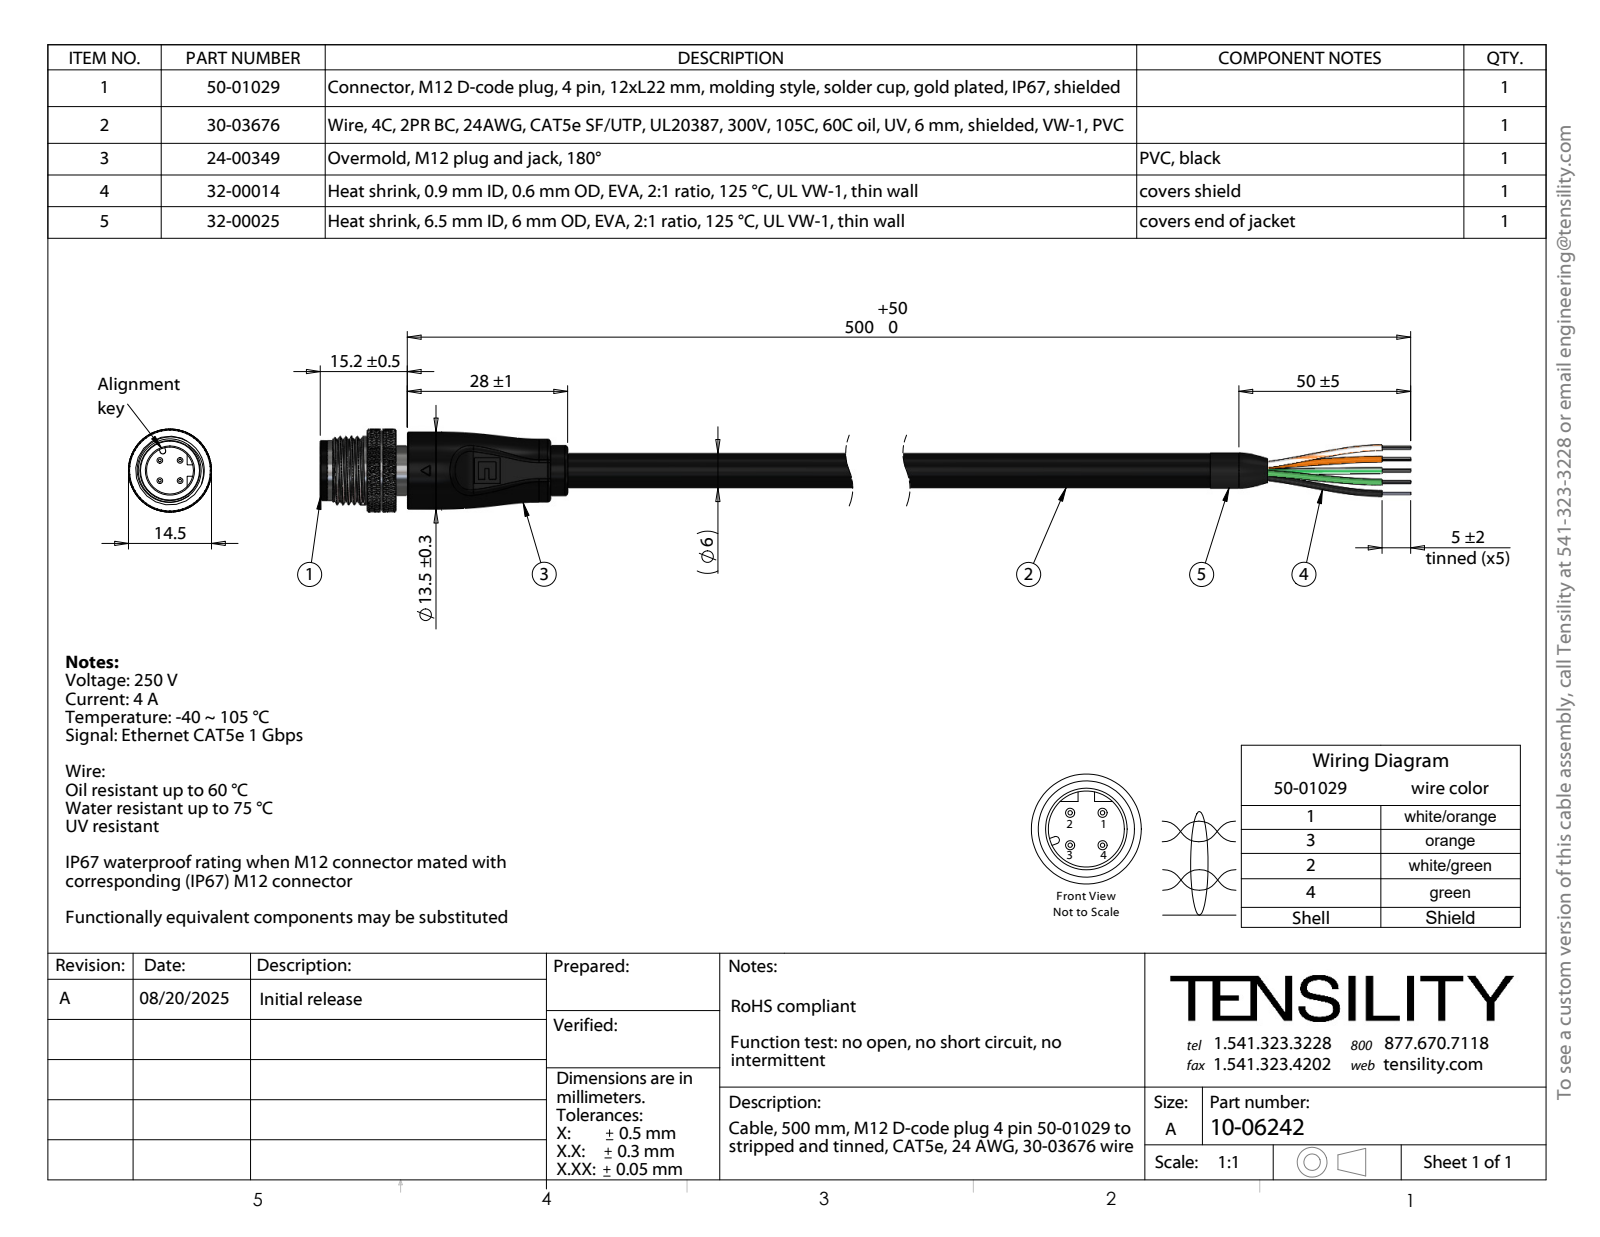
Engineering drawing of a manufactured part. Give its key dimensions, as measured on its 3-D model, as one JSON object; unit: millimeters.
{"part_name": "10-06242; 50-01029-03_默认; 50-01029-01_默认; 30-03676_s + t (+4 more)", "step_written_by": "SolidWorks 2025 (CONFIG_CONTROL_DESIGN)", "units": "millimeters", "bodies": {"solids": 86, "faces": 2792, "planar": 263, "cylindrical": 823, "other": 1706}, "overall_size": [223.2, 14.5, 14.5], "volume_mm3": 9287, "surface_area_mm2": 26453, "round_holes": [[0.2, 28], [1, 4], [1.05, 4], [3.16, 1], [3.21, 1], [3.36, 1], [8, 1], [8.2, 1], [8.8, 1], [9.5, 1]], "round_bosses_or_shafts": [[0.2, 35], [1.4, 4], [14.5, 1], [13.9, 1], [13.5, 1], [12, 1], [11, 1], [10.5, 1]], "partial_cylinders_radius": [[0.5, 2], [1.5, 2], [1.96, 2], [5, 1], [5.58, 1], [6.75, 1]], "face_to_face_distances": [180, 7, 2, 178, 5, 28, 30, 150, 10.8, 3.8], "hole_center_spacings": [1.91, 2.09, 1.06, 0.35, 0.89, 1.08, 1.24, 1.71]}
